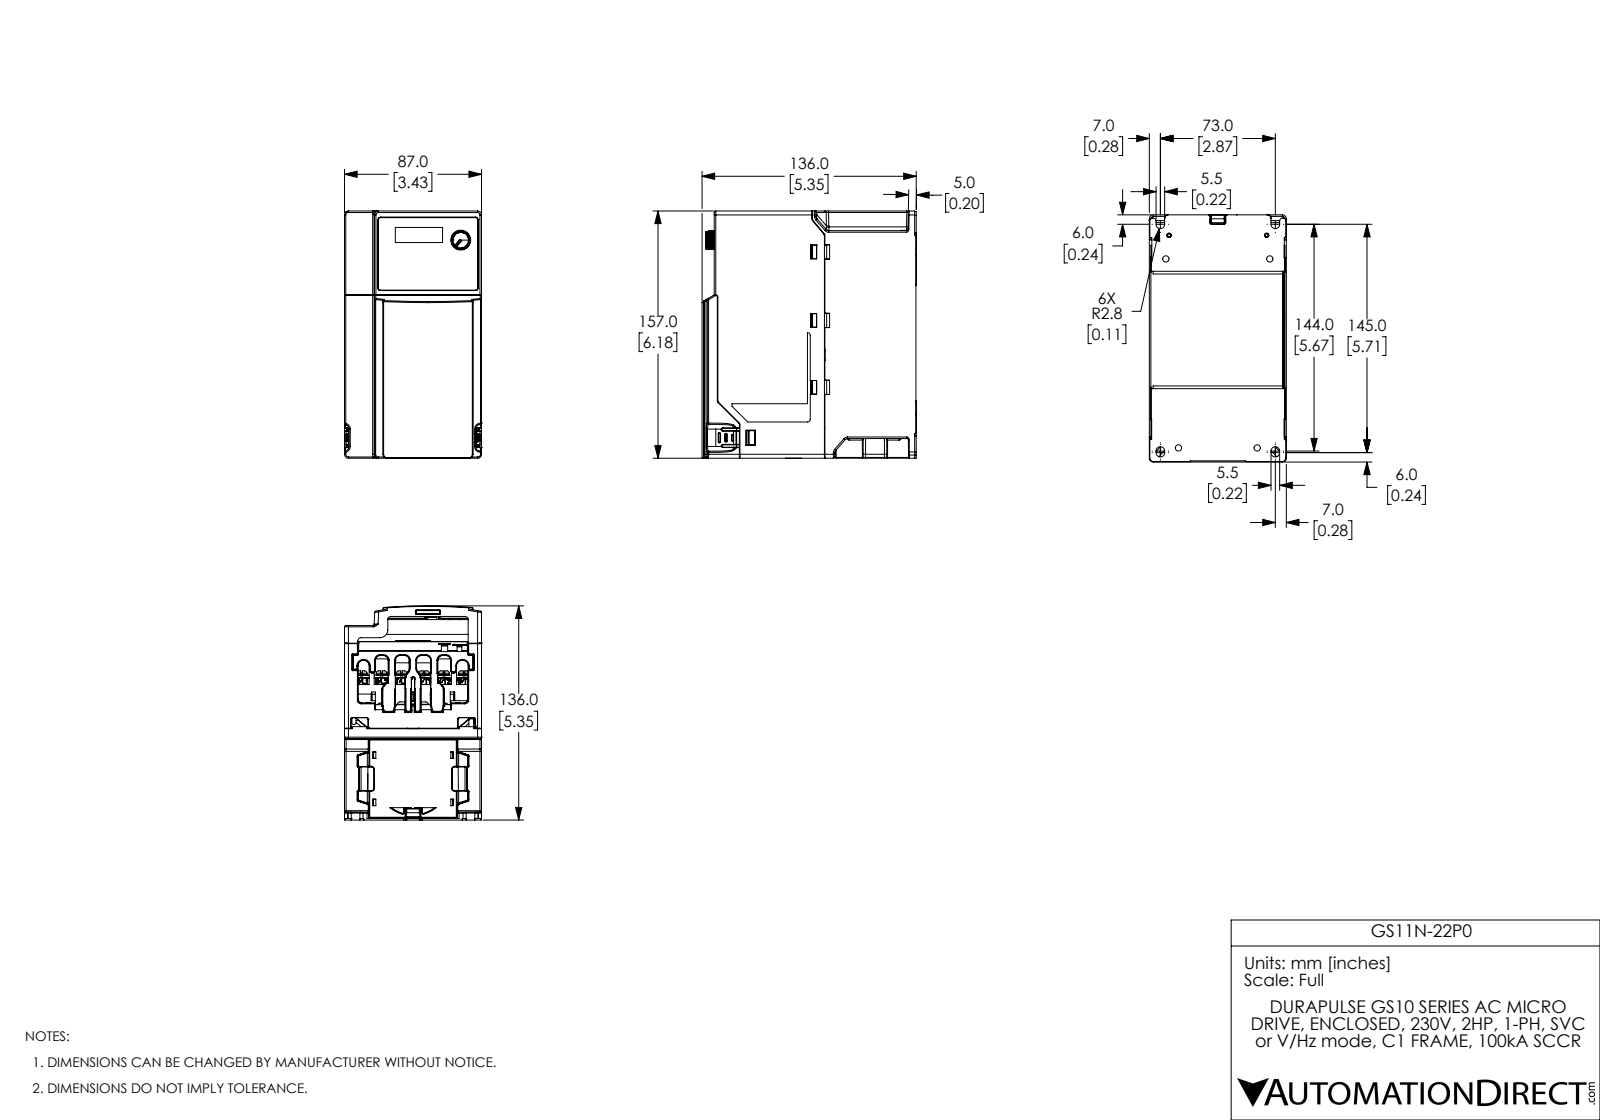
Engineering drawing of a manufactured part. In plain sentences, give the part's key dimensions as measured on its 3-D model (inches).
The part is named "DELTA_IA_MDS_VFD-ME300-C1_D-3D_20190924.X_T FRONT CASE COVER n BACK COMPLETE nc EXT2 red1 R1g fXT r1 ext 1b r3 Cb Coord". Its 3-D file was written by "SolidWorks 2017 (AUTOMOTIVE_DESIGN)". It is 7 solids with 4558 faces: 2468 planar, 1193 cylindrical and 897 other. Overall it measures 6.181 by 5.354 by 3.487 inches. Its volume is 63.1 cubic inches and its surface area 348 square inches. Round holes: 4 of diameter 0.157, 3 of diameter 0.079, 2 of diameter 0.11, 1 of diameter 0.496. Round bosses or shafts: 10 of diameter 0.268, 10 of diameter 0.157, 1 of diameter 0.509, 1 of diameter 0.471, 1 of diameter 0.43. Partial cylindrical surfaces (rounded edges, fillets, slot ends): 257 of radius 0.02, 169 of radius 0.012, 166 of radius 0.039, 36 of radius 0.079, 30 of radius 0.008, 26 of radius 0.028, 21 of radius 0.031, 21 of radius 0.059. The main face-to-face distances are 0.039, 3.425, 3.386, 1.902, 2.717, 0.354, 2.256, 4.972, 4.618, 0.394. The hole center spacings are 0.596, 2.588, 4.735, 5.247, 5.32, 5.754, 0.081, 0.428.
